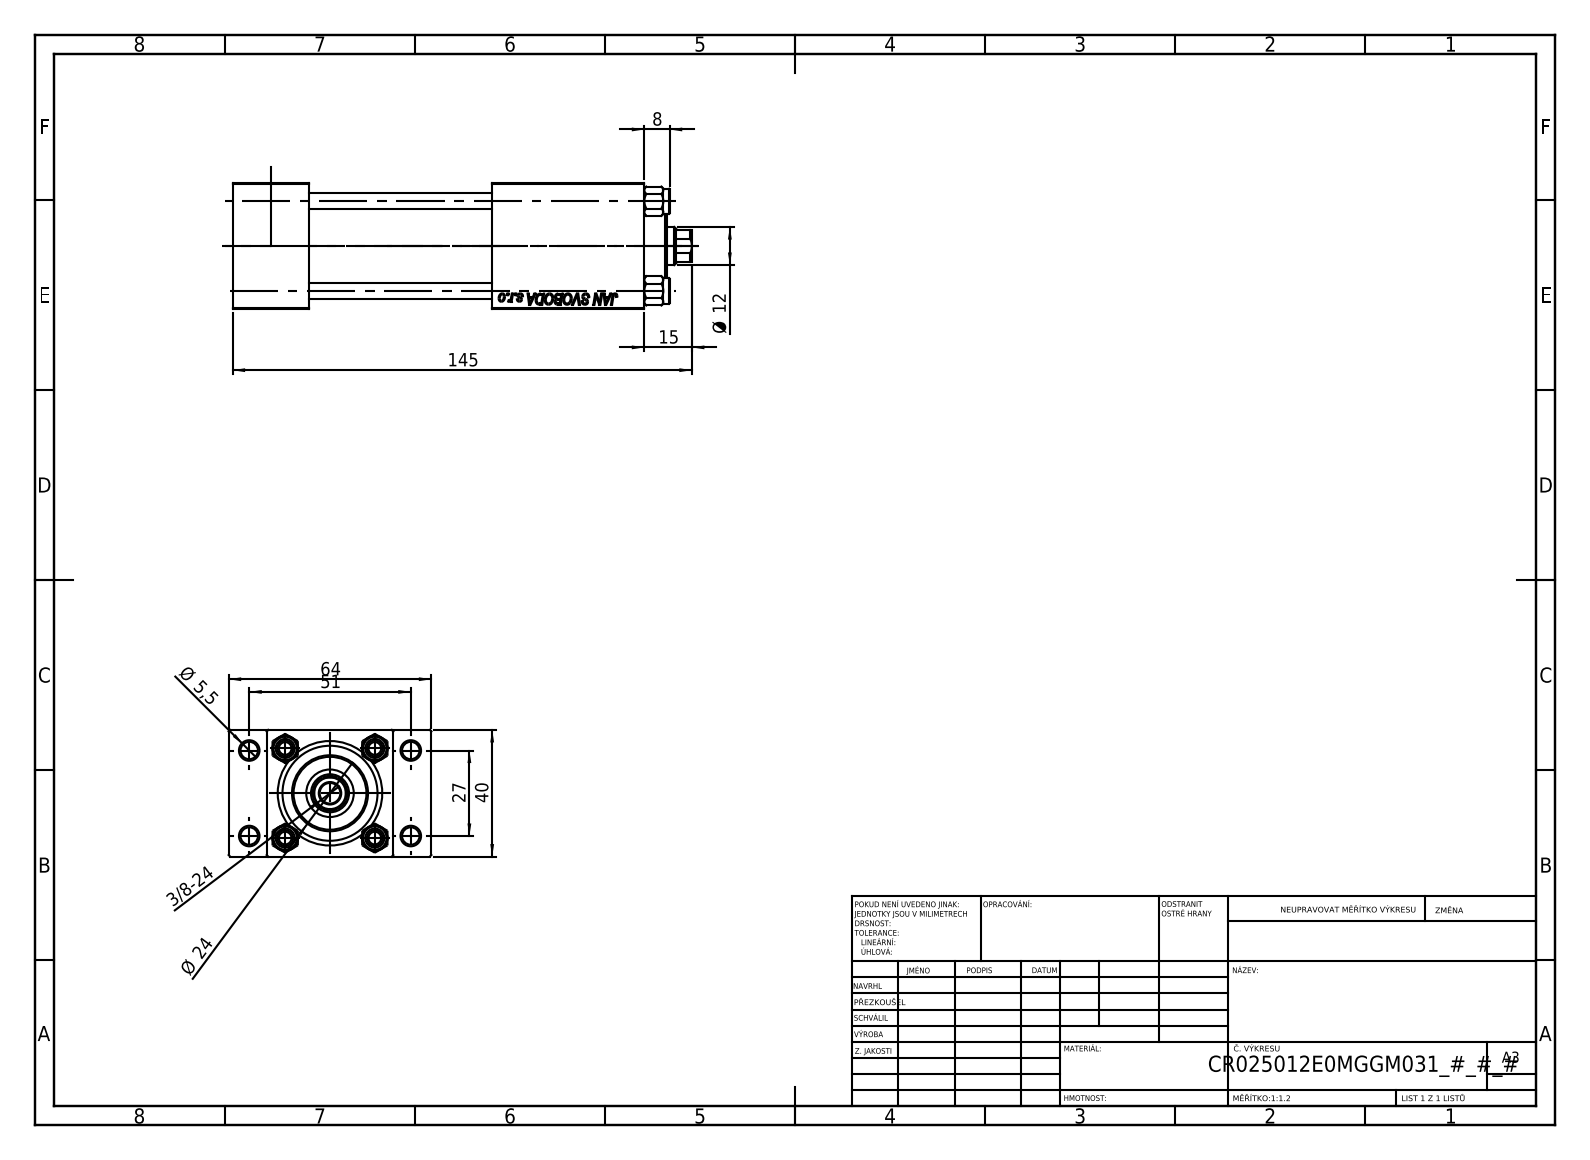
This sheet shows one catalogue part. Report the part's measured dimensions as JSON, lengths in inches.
{"part_name": "V215CR_TYCINKA_E; V215_VC_A; V215CR_E_Body; V215CR_VCP_E (+1 more)", "step_written_by": "SolidWorks 2019 (CONFIG_CONTROL_DESIGN)", "units": "inches", "bodies": {"solids": 11, "faces": 1136, "planar": 497, "cylindrical": 87, "other": 552}, "overall_size": [5.709, 2.52, 1.575], "volume_in3": 10.31, "surface_area_in2": 101, "round_holes": [[0.197, 4], [0.217, 4], [0.787, 3], [0.276, 2], [0.518, 2], [0.256, 1], [0.472, 1], [0.591, 1], [0.984, 1], [1.181, 1]], "round_bosses_or_shafts": [[0.315, 4], [1.22, 1], [0.945, 1]], "partial_cylinders_radius": [[0.217, 1]], "face_to_face_distances": [1.575, 0.945, 0.472, 2.047, 5.118, 4.173, 3.988, 3.043, 1.13, 2.52], "hole_center_spacings": [0.448, 0.788, 1.114, 1.136, 1.177, 1.561, 1.903, 1.063]}
